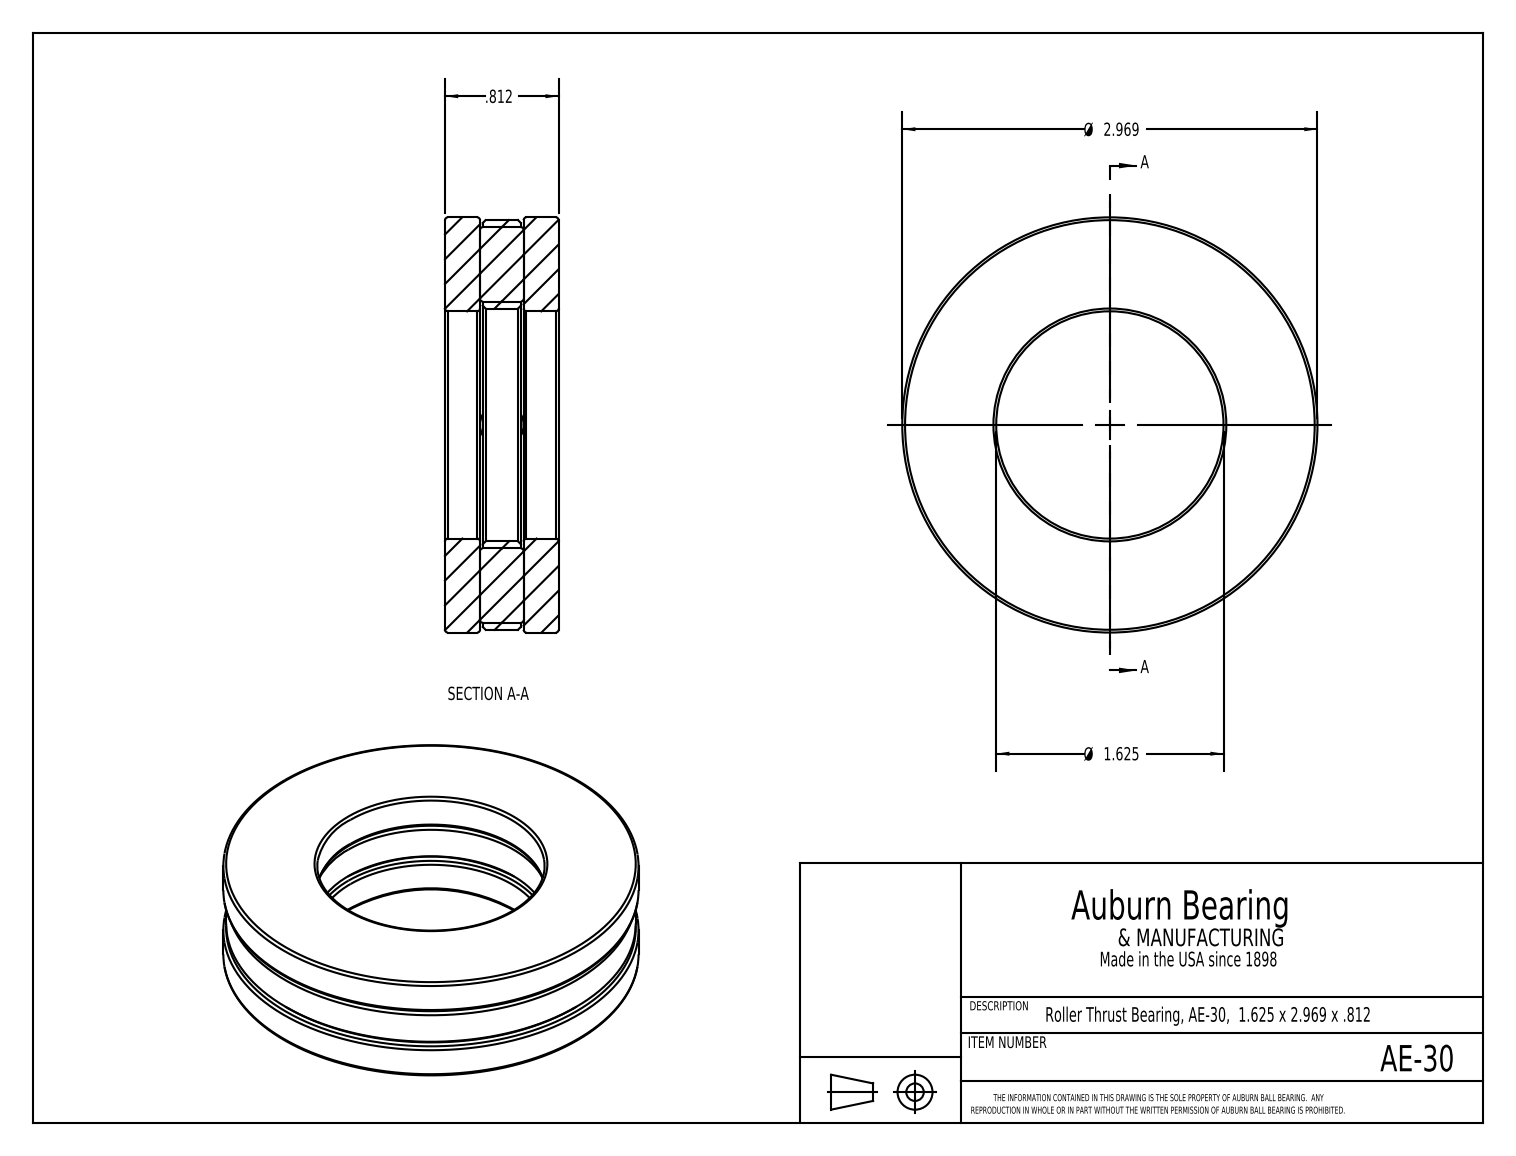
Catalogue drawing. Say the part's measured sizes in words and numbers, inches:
The part is named "AE-30". Its 3-D file was written by "SolidWorks 2017 (CONFIG_CONTROL_DESIGN)". It is 7 solids with 60 faces: 30 planar, 10 cylindrical and 20 other. Overall it measures 2.969 by 2.969 by 0.812 inches. Its volume is 3.635 cubic inches and its surface area 41.96 square inches. Round holes: 1 of diameter 1.625, 1 of diameter 1.625, 1 of diameter 1.665. Round bosses or shafts: 2 of diameter 0.312, 1 of diameter 2.969, 1 of diameter 2.929. The main face-to-face distances are 0.25, 0.562, 0.27, 0.542, 0.02, 0.292, 0.312, 0.812, 0.272, 0.727.
